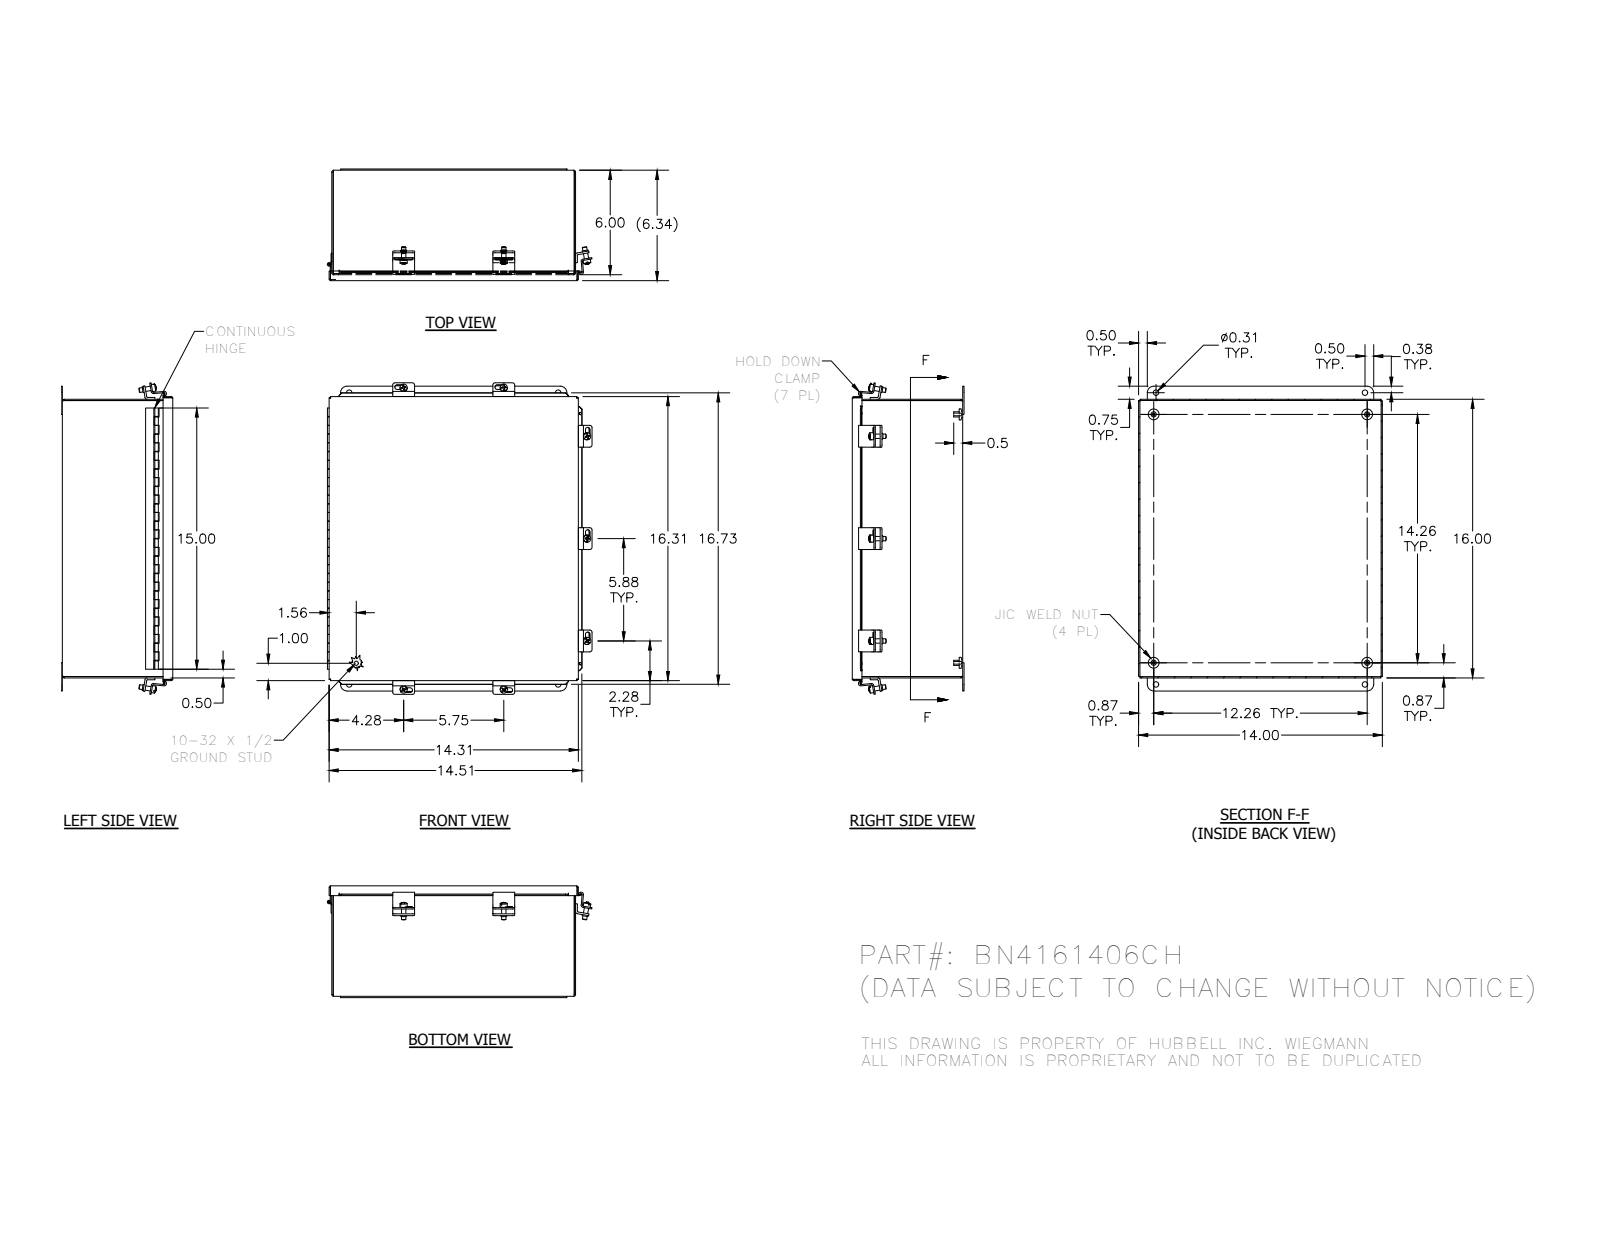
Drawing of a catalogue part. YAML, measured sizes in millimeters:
part_name: "B_1614CH_LID; 316169; 38811; 3499 (+8 more)"
step_written_by: "Autodesk Inventor 2016 (AUTOMOTIVE_DESIGN)"
units: millimeters
bodies: {solids: 20, faces: 547, planar: 349, cylindrical: 147, other: 51}
overall_size: [444.5, 383.18, 158.98]
volume: 1176000
surface_area: 1291000
round_holes:
  - {diameter: 3.96, count: 4}
  - {diameter: 7.87, count: 4}
  - {diameter: 3.56, count: 2}
  - {diameter: 4.98, count: 2}
  - {diameter: 2.96, count: 1}
round_bosses_or_shafts:
  - {diameter: 15.88, count: 4}
  - {diameter: 7.62, count: 4}
  - {diameter: 6.35, count: 3}
  - {diameter: 10.4, count: 2}
  - {diameter: 8.74, count: 2}
  - {diameter: 5.08, count: 1}
  - {diameter: 4.83, count: 1}
  - {diameter: 2.54, count: 1}
partial_cylinders:
  - {radius: 1.19, count: 8}
  - {radius: 3.07, count: 8}
  - {radius: 3.17, count: 8}
  - {radius: 1.98, count: 4}
  - {radius: 3.38, count: 4}
  - {radius: 3.48, count: 4}
  - {radius: 9.53, count: 4}
  - {radius: 0.79, count: 3}
face_to_face_distances: [1.88, 155.58, 1.5, 157.08, 153.7, 155.2, 353.72, 404.52, 355.6, 351.84]
hole_center_spacings: [31.91, 393.71, 499.85, 304.8, 309.6, 309.61, 311.15, 361.95]
